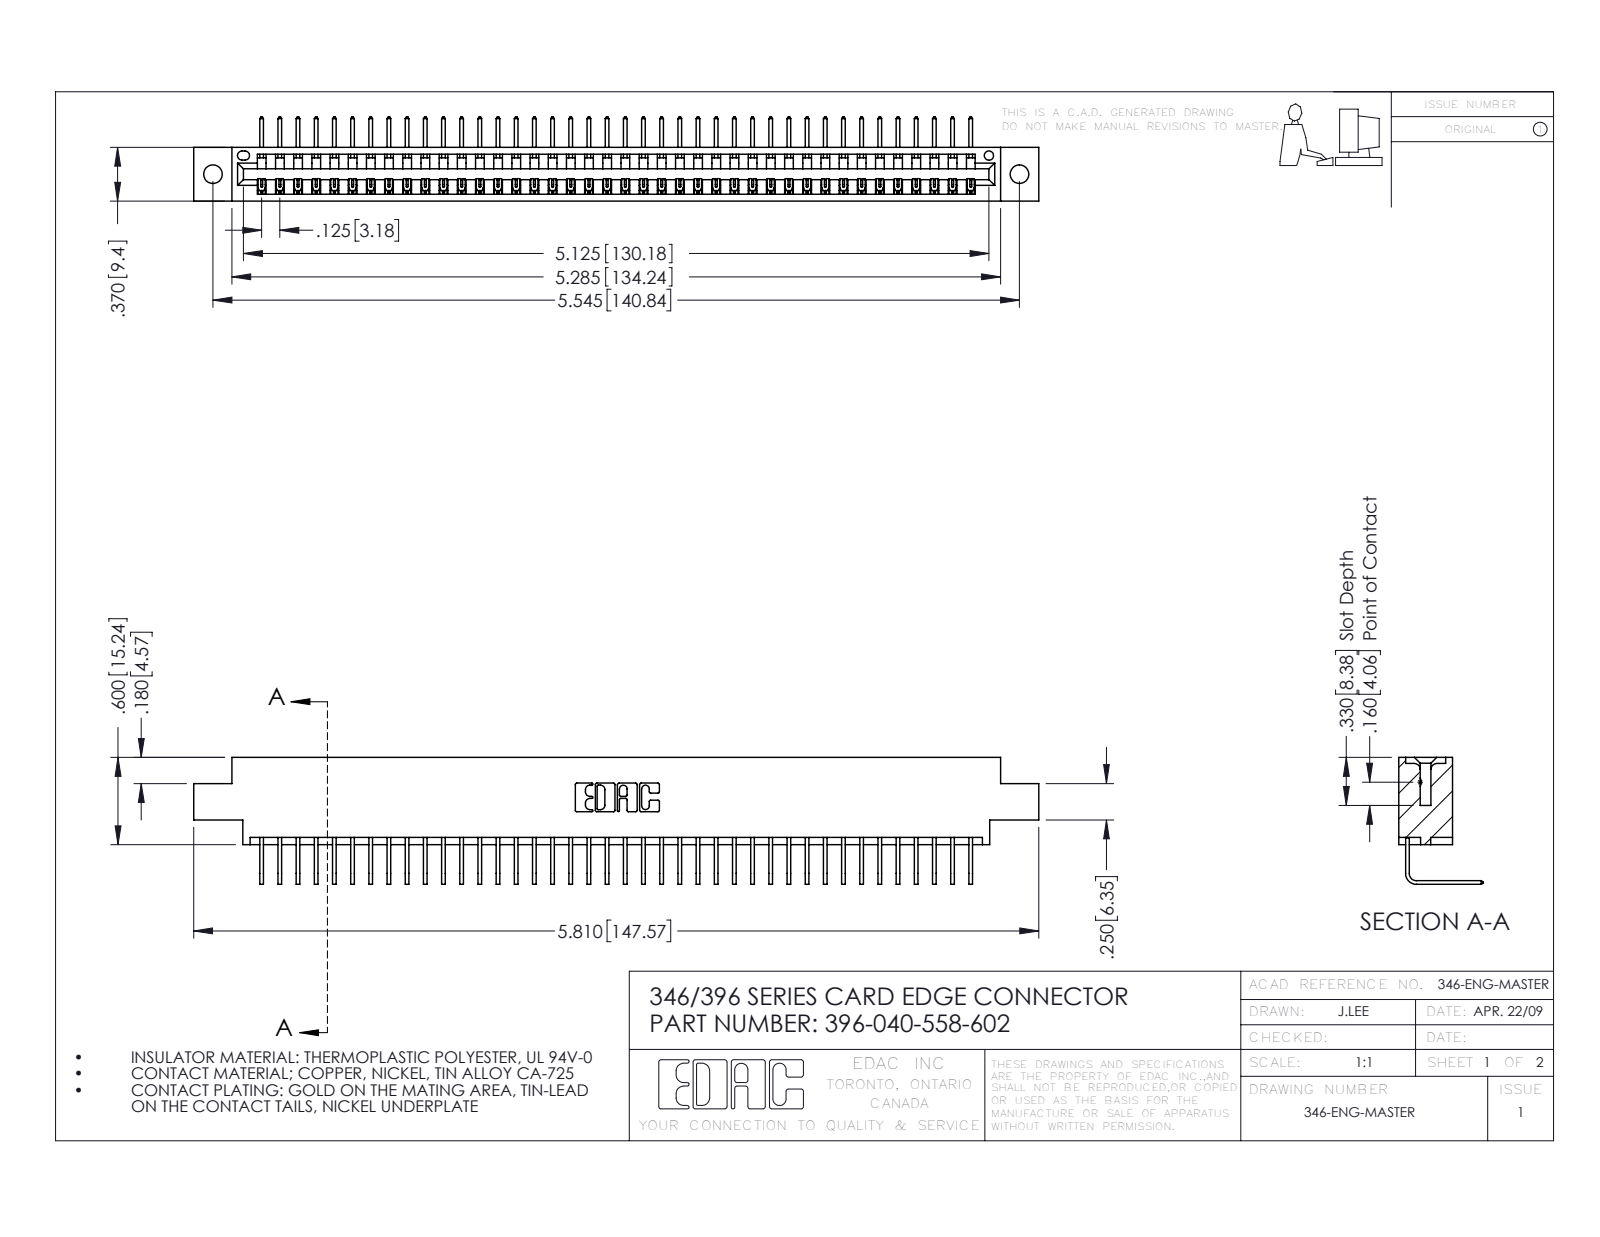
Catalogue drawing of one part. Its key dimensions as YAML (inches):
part_name: "346 Part_0.170 Offset - 0.128 Dia; 396-040-558-602; 345-292-001_558 Tail - 2"
step_written_by: "SolidWorks 2016 (CONFIG_CONTROL_DESIGN)"
units: inches
bodies: {solids: 41, faces: 2526, planar: 1760, cylindrical: 766, other: 0}
overall_size: [5.81, 0.873, 0.58]
volume: 0.858
surface_area: 28.25
round_holes:
  - {diameter: 0.128, count: 2}
  - {diameter: 0.064, count: 1}
partial_cylinders:
  - {radius: 0.006, count: 80}
  - {radius: 0.01, count: 22}
  - {radius: 0.007, count: 6}
  - {radius: 0.031, count: 6}
  - {radius: 0.026, count: 3}
  - {radius: 0.031, count: 2}
  - {radius: 0.04, count: 2}
  - {radius: 0.014, count: 1}
face_to_face_distances: [0.322, 0.048, 0.37, 0.25, 0.298, 0.025, 0.072, 0.148, 0.222, 0.1]
hole_center_spacings: [0.246, 5.336, 5.545]
